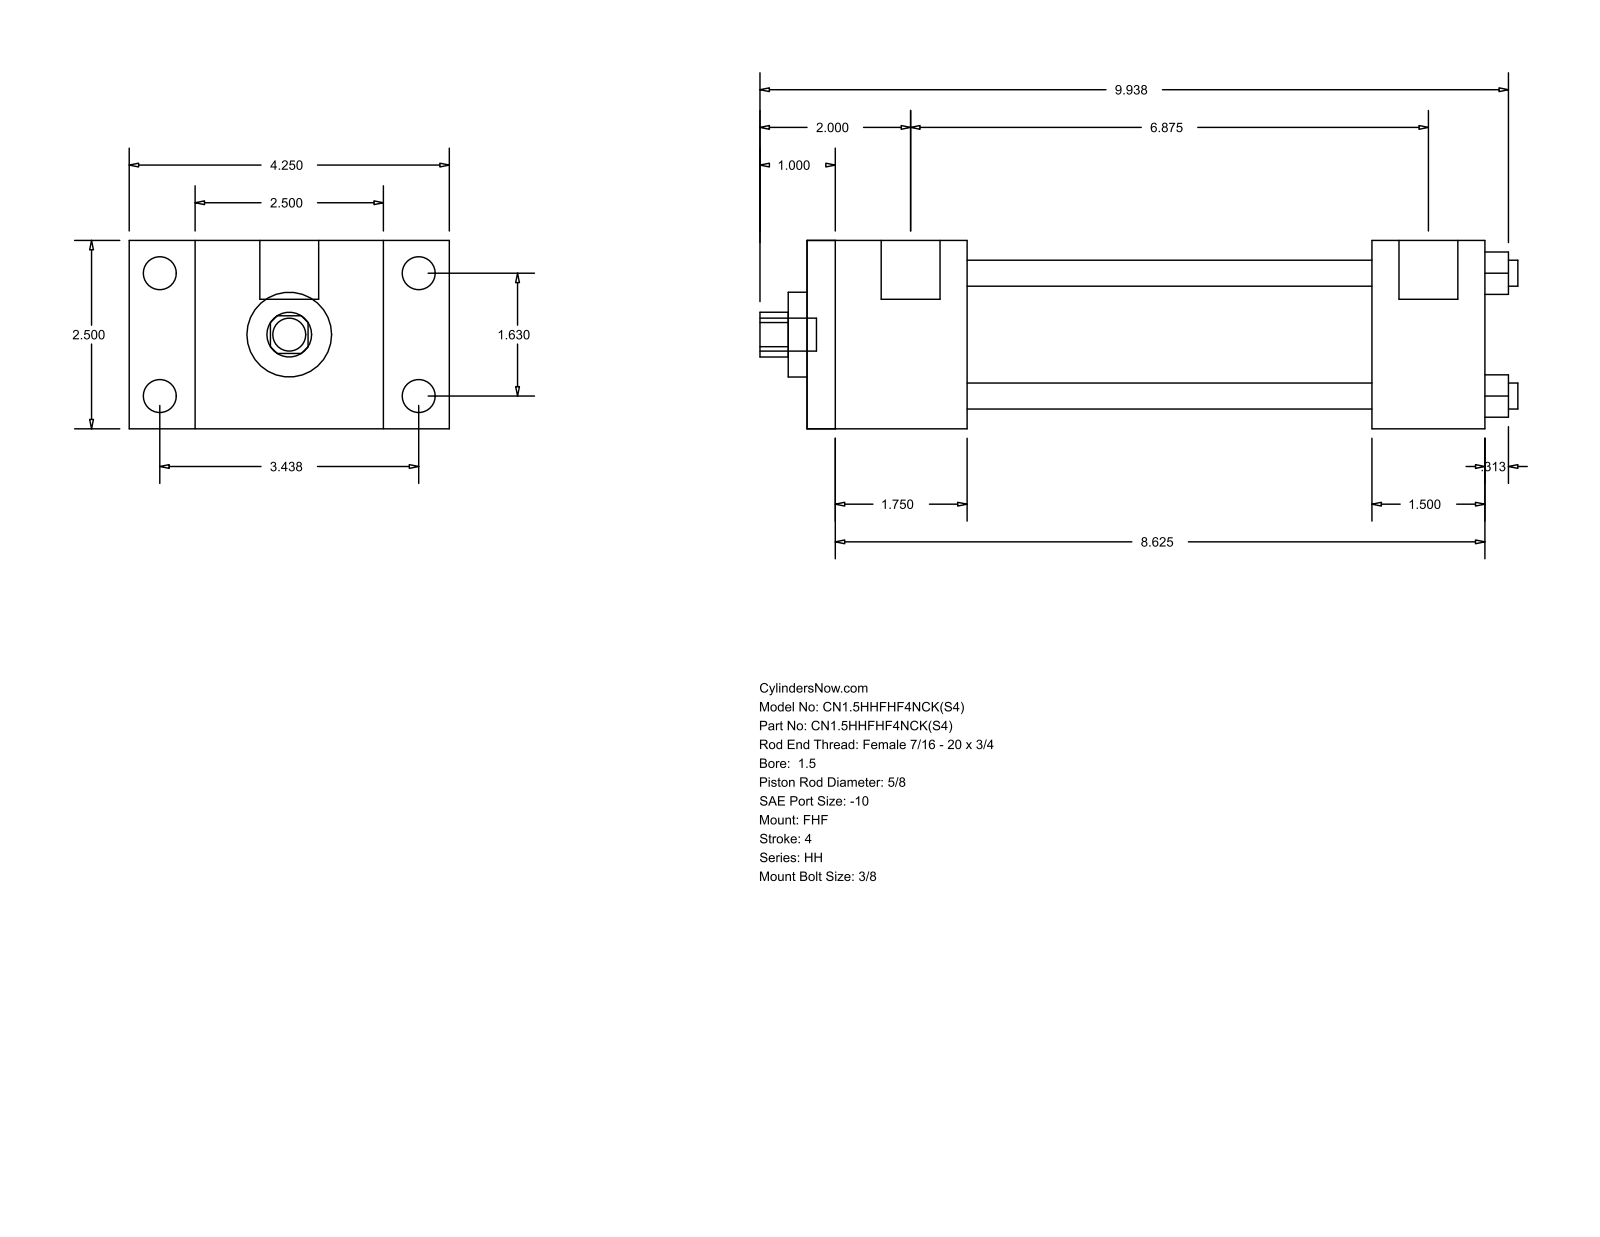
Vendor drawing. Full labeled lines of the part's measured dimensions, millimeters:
Part name (STEP PRODUCT): HH_FHF__0150_0.625
STEP written by: GSSL Pune (CONFIG_CONTROL_DESIGN)
Units: millimetres
Bodies: 0 solids, 88 faces (60 planar, 28 cylindrical, 0 other)
Overall size (bounding box): 255.59 × 107.95 × 63.5
Round holes (diameter × count): ⌀8.76 ×4, ⌀15.88 ×1, ⌀28.57 ×1, ⌀44.45 ×1
Round bosses / shafts (diameter × count): ⌀11.13 ×4, ⌀5.56 ×4, ⌀19.84 ×2, ⌀11.11 ×1
Partial cylindrical surfaces — rounded edges, fillets, slot ends (radius × count): R7.54 ×1
Main face-to-face distances: 63.5, 22.23, 85.73, 53.97, 107.96, 228.59, 174.62, 190.5, 136.53, 38.09
Hole centre spacings: 29.27, 41.4, 58.55
